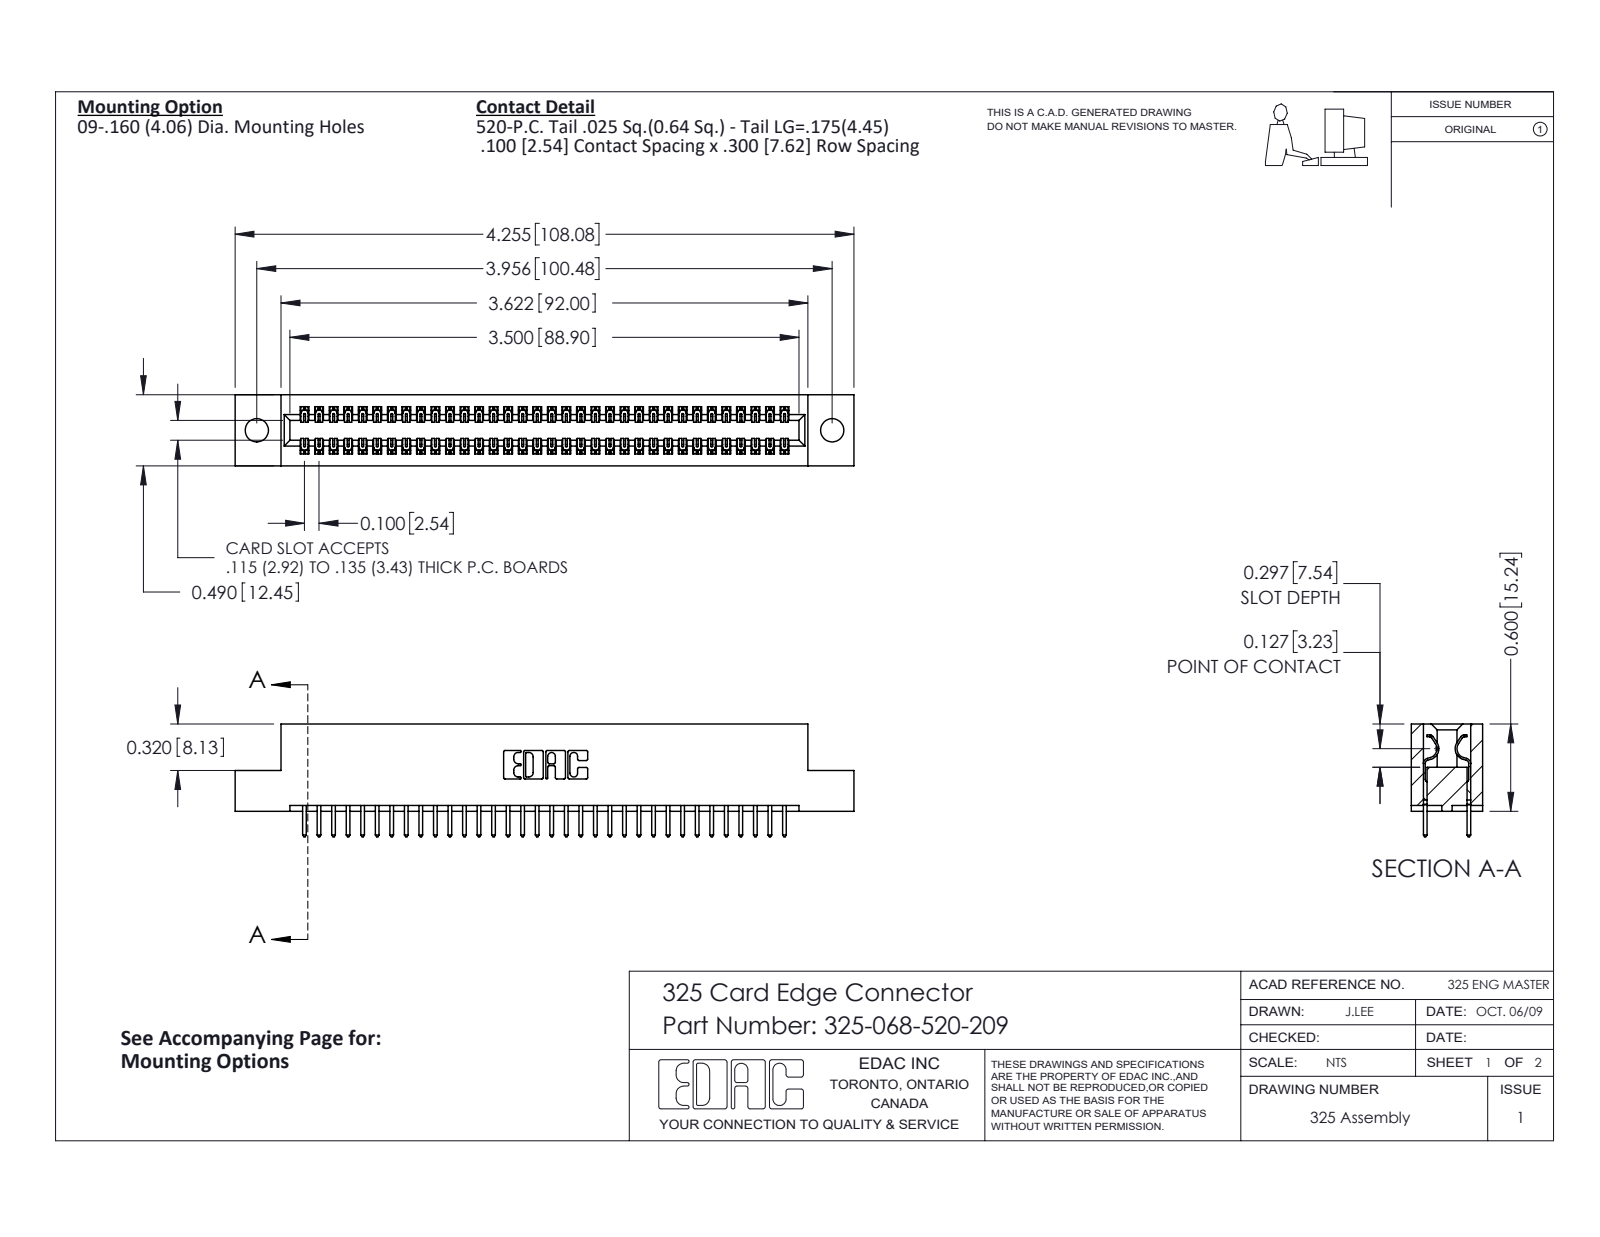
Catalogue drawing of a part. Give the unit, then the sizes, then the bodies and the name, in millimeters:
Units: millimetres
Overall size (bounding box): 108.1 × 19.7 × 12.4
Round holes (diameter × count): ⌀4.1 ×2
Partial cylindrical surfaces — rounded edges, fillets, slot ends (radius × count): R0.2 ×102, R0.3 ×68, R0.3 ×22, R0.2 ×6, R0.8 ×6, R0.7 ×3, R0.4 ×2, R0.6 ×2
Main face-to-face distances: 2.1, 10.3, 7.6, 12.4, 2.7, 9.7, 0.6, 8.3, 1, 7
Hole centre spacings: 100.5
Volume: 13 600 mm³ · Surface area: 16 100 mm²
Bodies: 69 solids, 3650 faces (2518 planar, 1132 cylindrical, 0 other)
Part name (STEP PRODUCT): 325-292-001_325-293-120; 325-068-520-209; 325 Part_.160 TH
STEP written by: SolidWorks 2016 (CONFIG_CONTROL_DESIGN)
